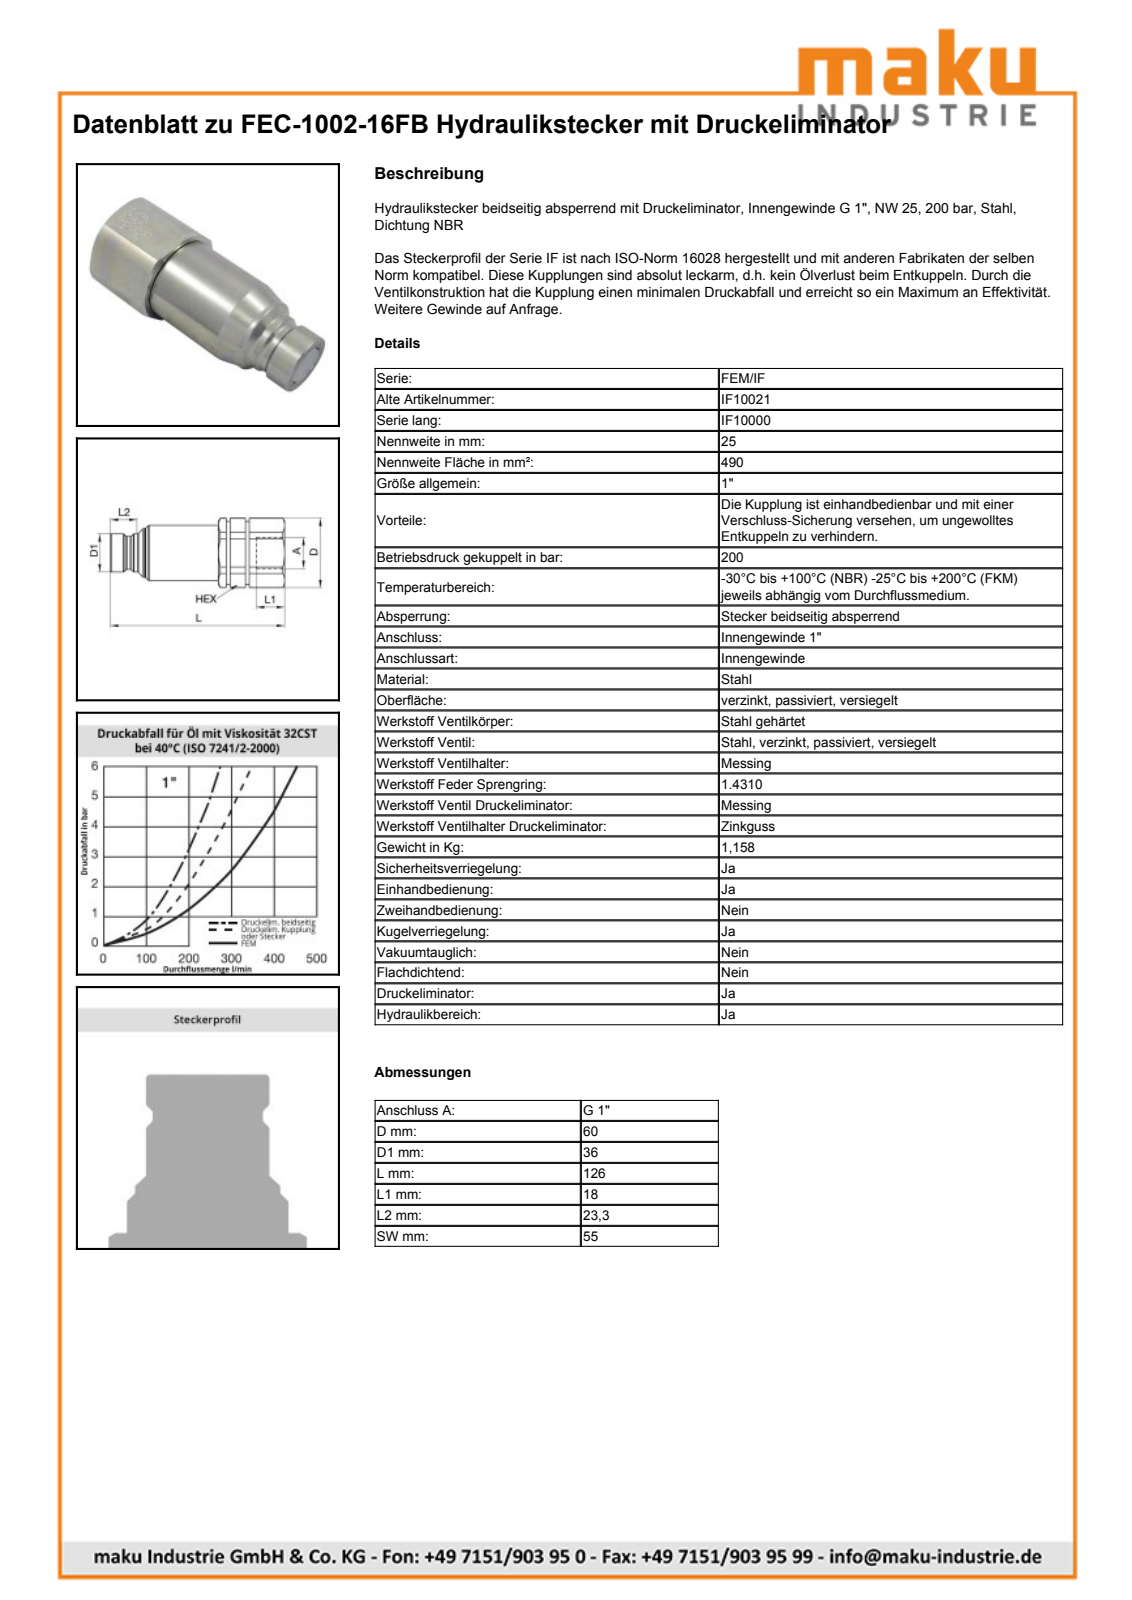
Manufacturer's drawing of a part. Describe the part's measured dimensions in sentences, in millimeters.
The part is named "FEC-1002-16FB". Its 3-D file was written by "SolidWorks 2009 (AUTOMOTIVE_DESIGN)". It is 7 solids with 331 faces: 66 planar, 99 cylindrical and 166 other. Overall it measures 126.26 by 60 by 55 millimeters. Its volume is 275 804 cubic millimeters and its surface area 73 034 square millimeters. Round holes: 1 of diameter 1.5, 1 of diameter 9.22, 1 of diameter 23.48, 1 of diameter 23.7, 1 of diameter 28.1, 1 of diameter 29, 1 of diameter 29.9, 1 of diameter 30.3, 1 of diameter 31.65, 1 of diameter 33.5, 1 of diameter 36.15, 1 of diameter 37.2. Round bosses or shafts: 1 of diameter 50, 1 of diameter 49.78, 1 of diameter 46, 1 of diameter 45.3, 1 of diameter 45.01, 1 of diameter 43.8, 1 of diameter 41.7, 1 of diameter 36. Partial cylindrical surfaces (rounded edges, fillets, slot ends): 8 of radius 0.5, 1 of radius 6, 1 of radius 30. The main face-to-face distances are 55, 24, 6.7, 30.7, 2, 92.82, 99.52, 123.52, 0.73, 93.55.
